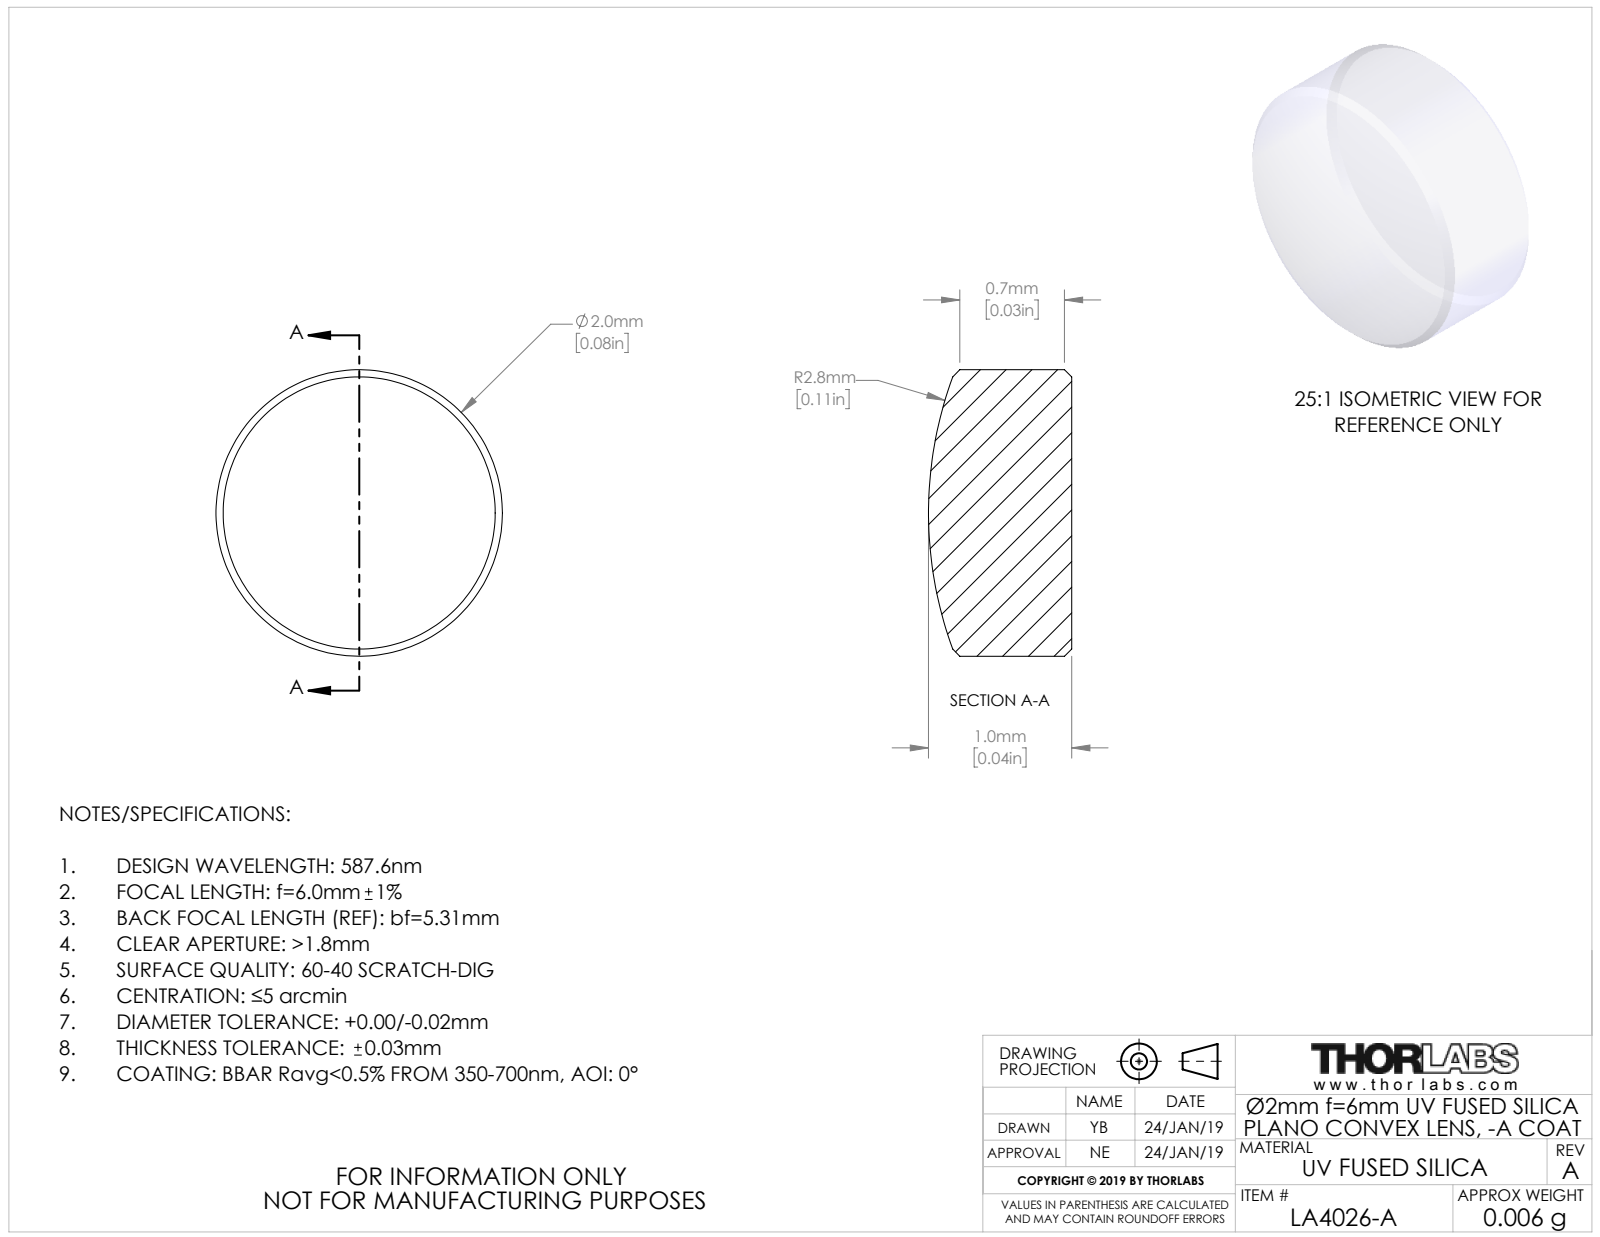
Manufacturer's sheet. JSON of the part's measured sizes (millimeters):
{"part_name": "TTN162804-E0W", "step_written_by": "SolidWorks 2018 (CONFIG_CONTROL_DESIGN)", "units": "millimeters", "bodies": {"solids": 1, "faces": 9, "planar": 1, "cylindrical": 2, "other": 6}, "overall_size": [2, 2, 1], "volume_mm3": 3, "surface_area_mm2": 11, "round_bosses_or_shafts": [[2, 1]]}
